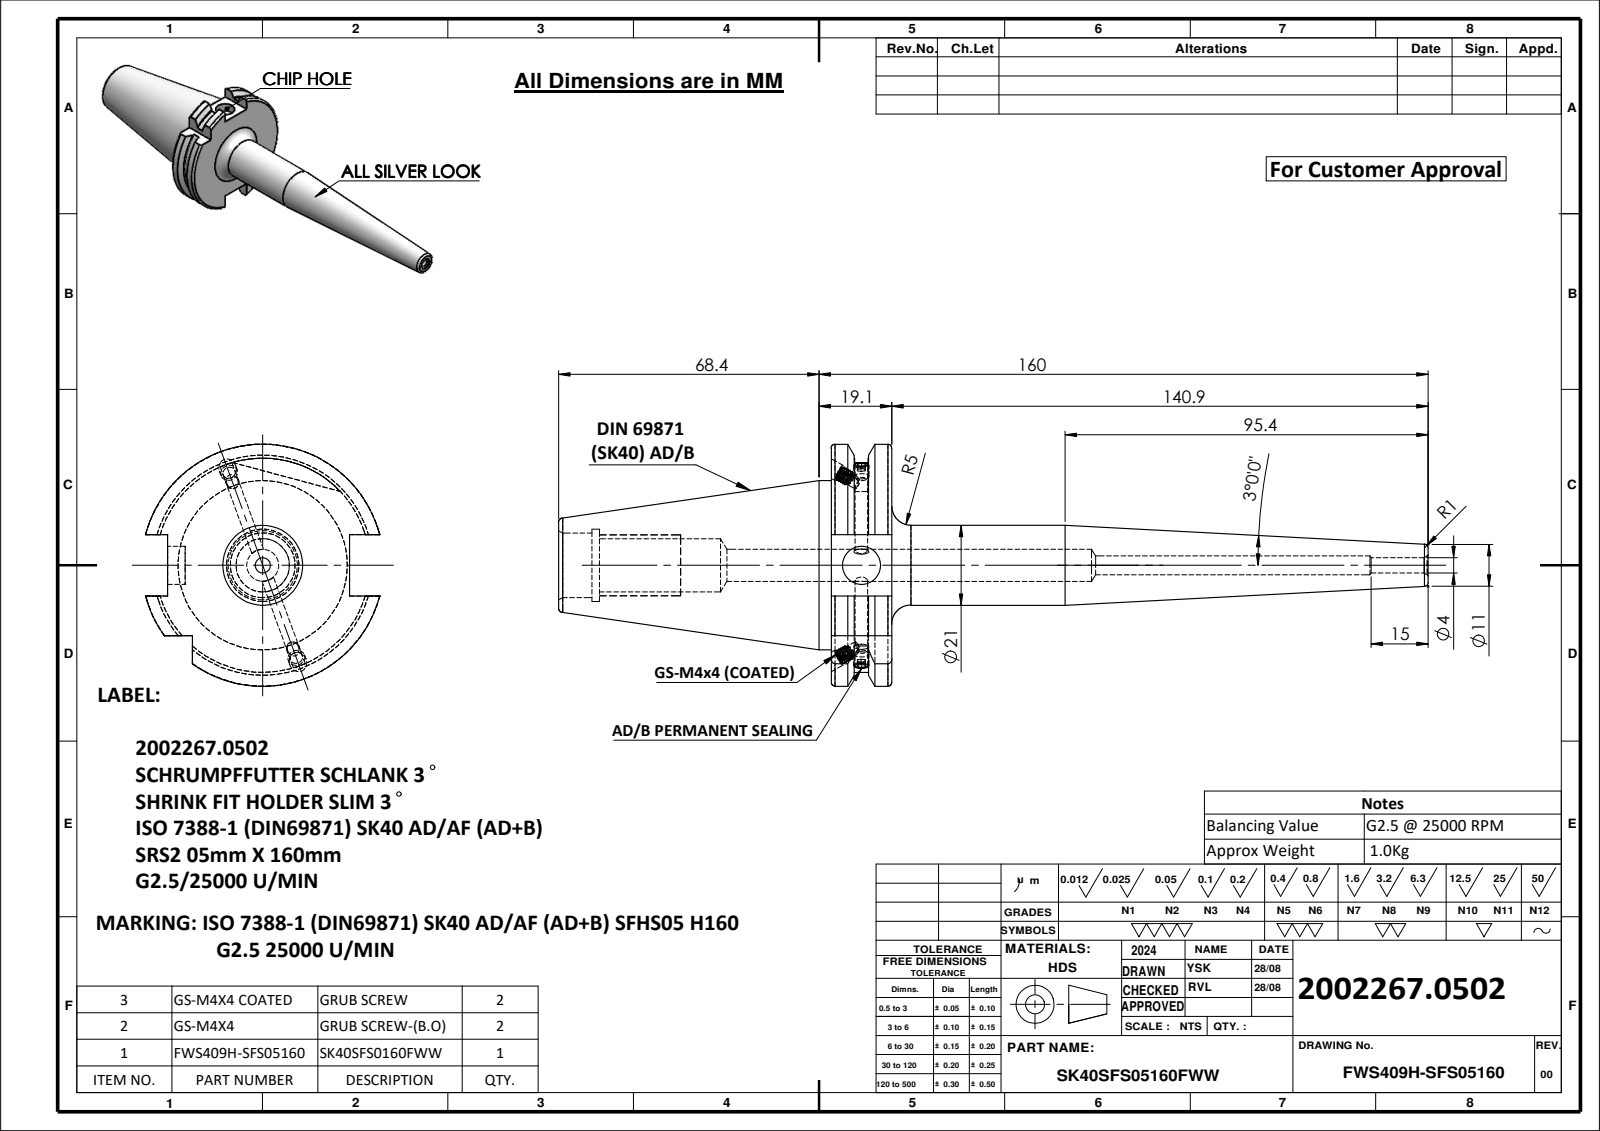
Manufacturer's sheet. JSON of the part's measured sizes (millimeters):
{"part_name": "SK40SFS05160FWW; GS-M4X4-COATING_DIN 913 - M4 x 4-N; GS-M4X4_DIN 913 - M4 x 4-N; FWS409H-SFS05160", "step_written_by": "SolidWorks 2024 (CONFIG_CONTROL_DESIGN)", "units": "millimeters", "bodies": {"solids": 5, "faces": 244, "planar": 62, "cylindrical": 70, "other": 112}, "overall_size": [228.4, 63.55, 61.48], "volume_mm3": 134152, "surface_area_mm2": 31238, "round_holes": [[3.3, 3], [4.5, 2], [4, 1], [5, 1], [8.4, 1], [10, 1], [14, 1], [17, 1], [19, 1]], "round_bosses_or_shafts": [[4, 4], [2.9, 2], [44.45, 1], [21, 1]], "partial_cylinders_radius": [[28.12, 1], [31.77, 1]], "face_to_face_distances": [15.9, 16.1, 47.8, 71.6, 87.5, 10.7, 60.9, 76.8, 77.62, 66.92]}
